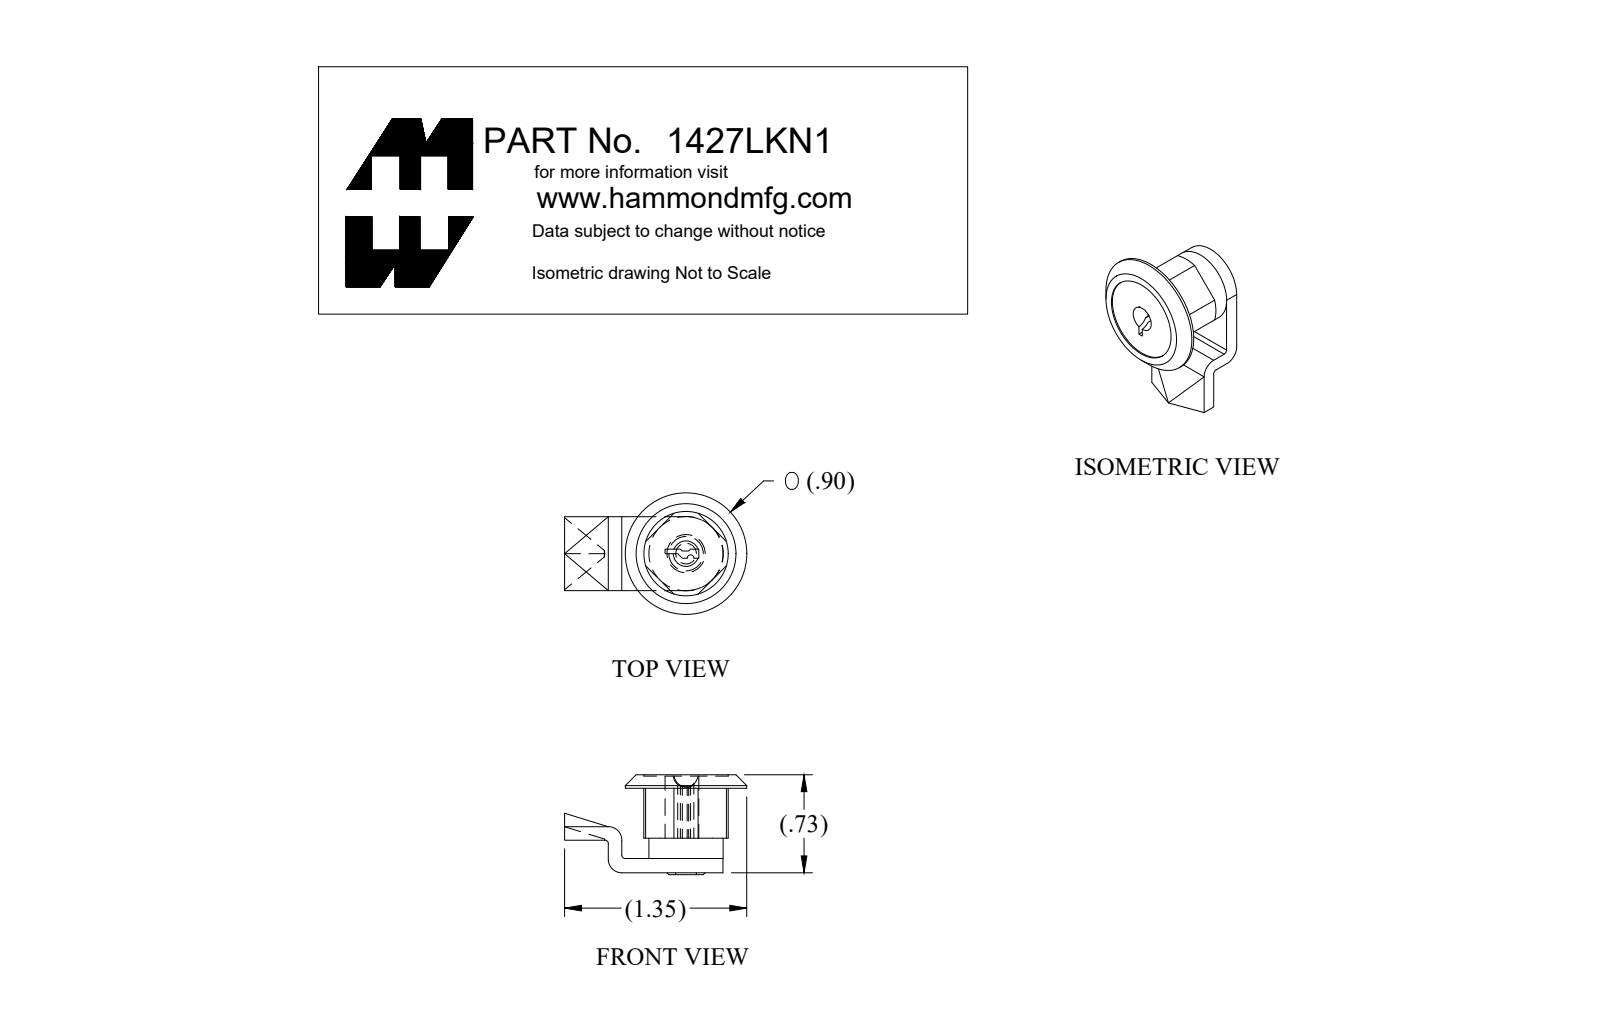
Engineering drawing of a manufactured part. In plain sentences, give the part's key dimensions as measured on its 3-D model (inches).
The part is named "1427LKN1". Its 3-D file was written by "SolidWorks 2019 (AUTOMOTIVE_DESIGN)". It is 1 solid with 58 faces: 40 planar, 14 cylindrical and 4 other. Overall it measures 1.35 by 0.9 by 0.74 inches. Its volume is 0.262 cubic inches and its surface area 4.049 square inches. Round holes: 1 of diameter 0.153. Round bosses or shafts: 1 of diameter 0.9, 1 of diameter 0.625, 1 of diameter 0.55. Partial cylindrical surfaces (rounded edges, fillets, slot ends): 2 of radius 0.025, 2 of radius 0.1, 1 of radius 0.025, 1 of radius 0.274. The main face-to-face distances are 0.626, 0.09, 0.716, 0.55, 0.1, 0.61, 0.52, 0.106, 0.62, 0.726.
